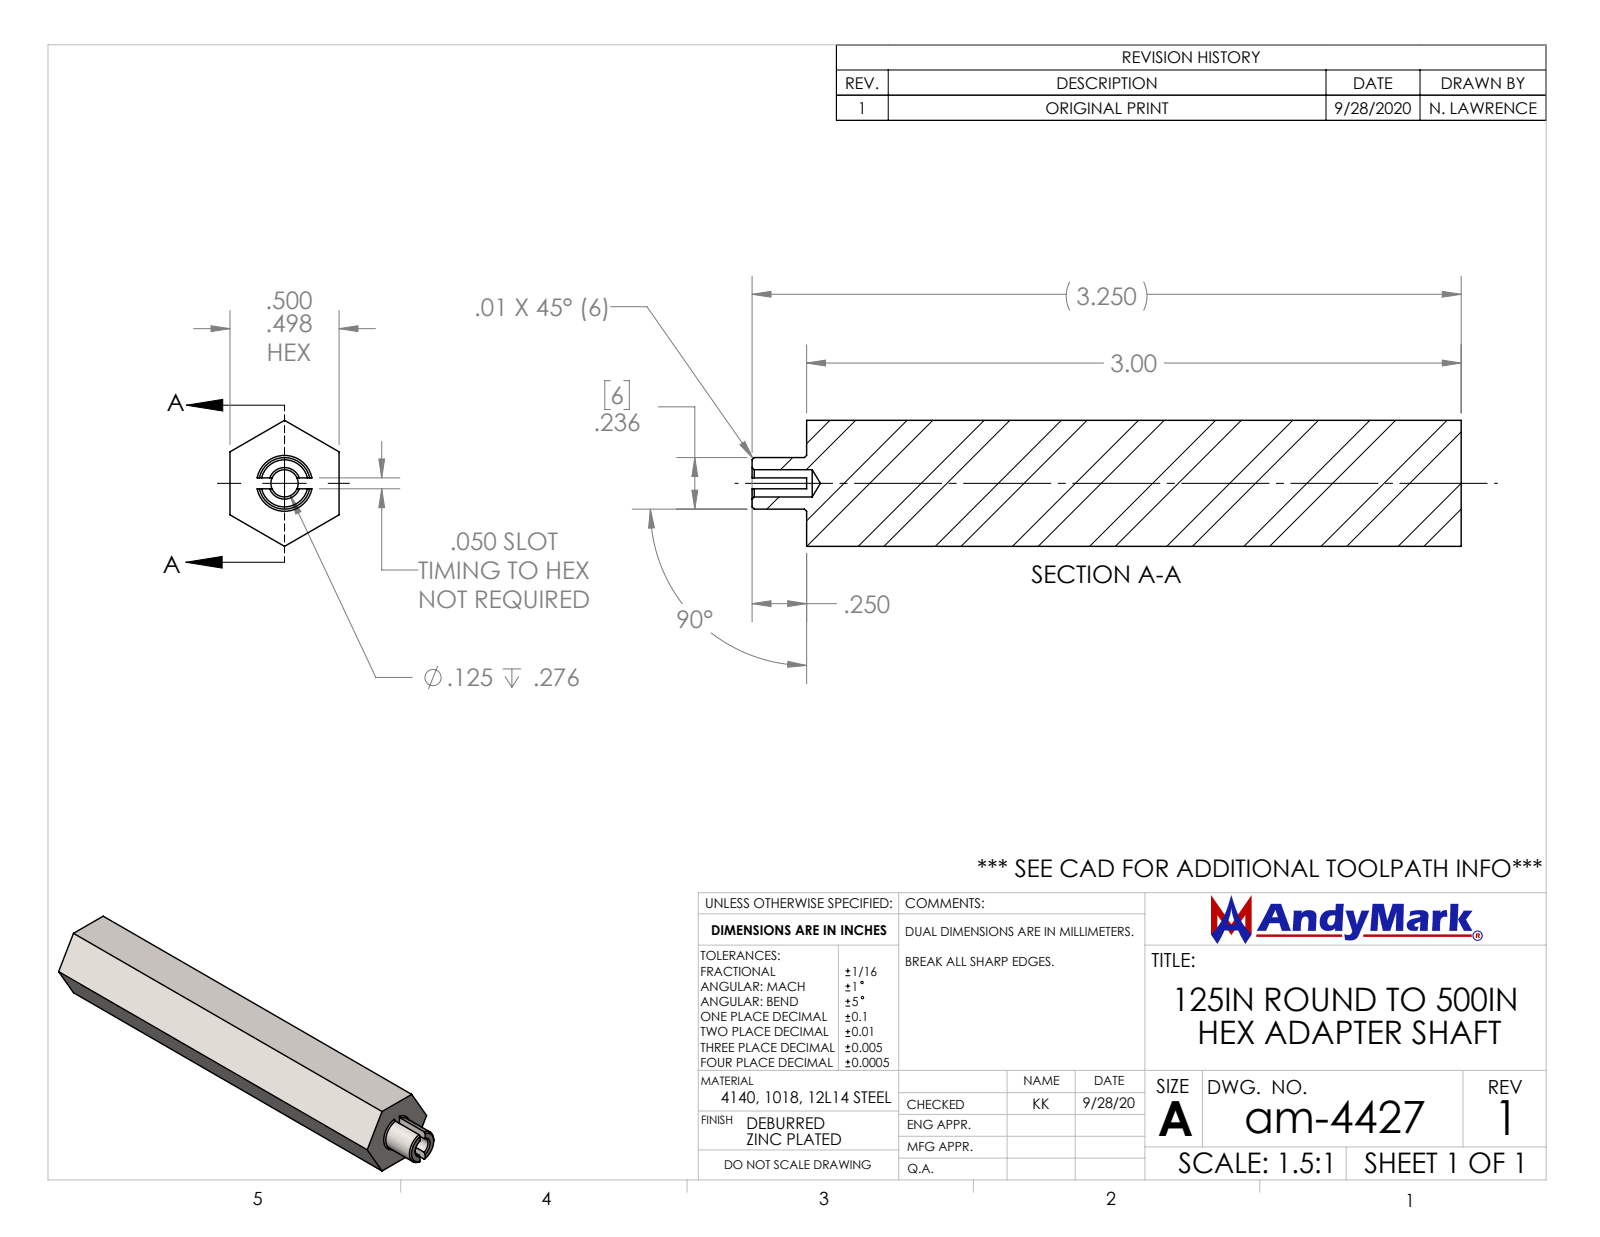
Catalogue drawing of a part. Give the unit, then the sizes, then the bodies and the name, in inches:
Units: inches
Overall size (bounding box): 3.25 × 0.577 × 0.5
Round holes (diameter × count): ⌀0.125 ×1
Round bosses / shafts (diameter × count): ⌀0.236 ×1
Main face-to-face distances: 0.5, 3, 0.05, 3.25, 0.25
Volume: 0.656 in³ · Surface area: 5.923 in²
Bodies: 1 solid, 24 faces (14 planar, 3 cylindrical, 7 other)
Part name (STEP PRODUCT): am-4427 125IN Round to 500IN Hex Adapter Shaft
STEP written by: SolidWorks 2019 (AUTOMOTIVE_DESIGN)
